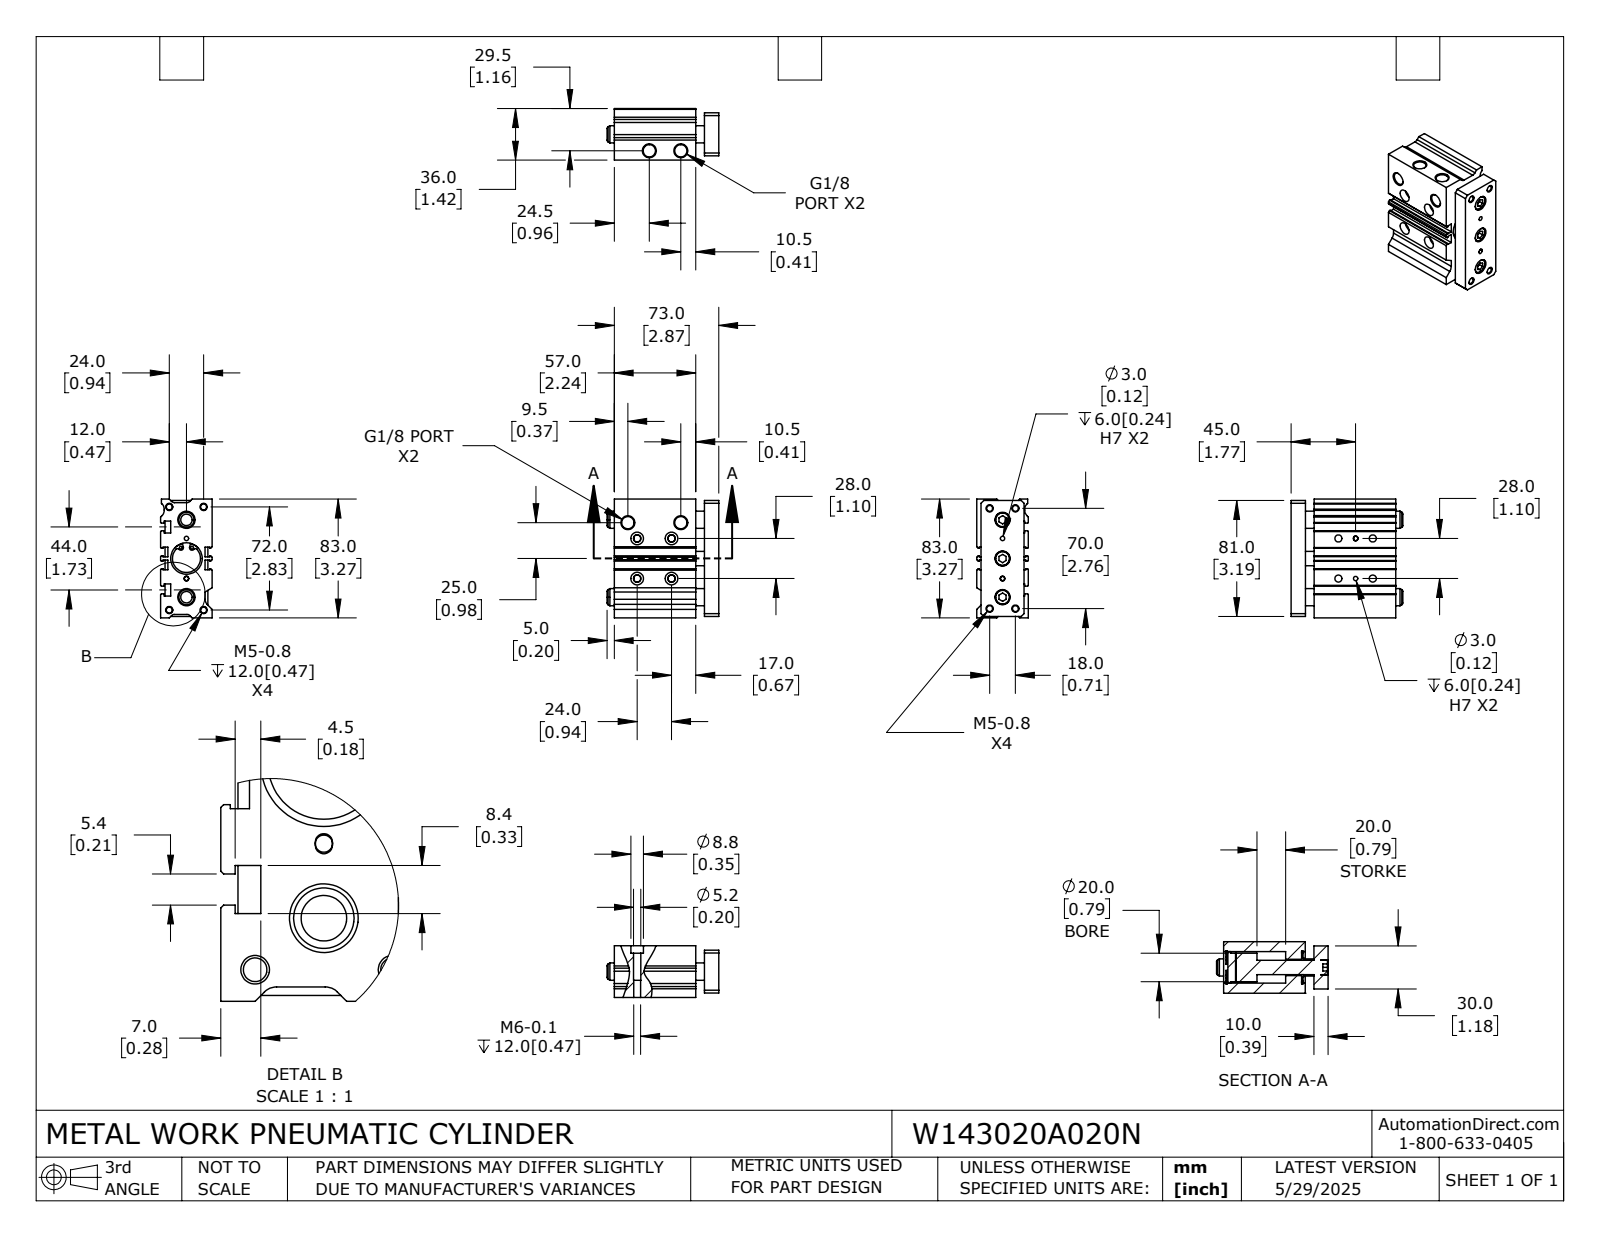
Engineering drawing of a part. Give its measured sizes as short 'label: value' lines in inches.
name: W143020A020N; W143020A020N_ROD; W143020A020N_BODY
written by: SolidWorks 2024 (CONFIG_CONTROL_DESIGN)
unit: in
bodies: 5 solids, 351 faces (172 planar, 141 cylindrical, 38 other)
size: 3.268 × 3.071 × 1.417
volume: 9.757 in³; area: 83.48 in²
holes: 8× ⌀0.163, 4× ⌀0.079, 4× ⌀0.118, 4× ⌀0.205, 4× ⌀0.337, 4× ⌀0.346, 3× ⌀0.413, 2× ⌀0.194, 2× ⌀0.194, 2× ⌀0.472, 1× ⌀0.449, 1× ⌀0.767
bosses: 3× ⌀0.394, 2× ⌀0.906, 1× ⌀0.787, 1× ⌀0.512
rounds: 4× R0.053, 4× R0.059, 4× R0.071, 4× R0.118, 3× R0.197
face distances: 0.079, 1.417, 0.098, 0.197, 0.394, 0.236, 0.63, 0.118, 2.874, 2.48
hole spacings: 0.124, 0.296, 0.336, 0.472, 0.474, 0.591, 0.78, 0.828
